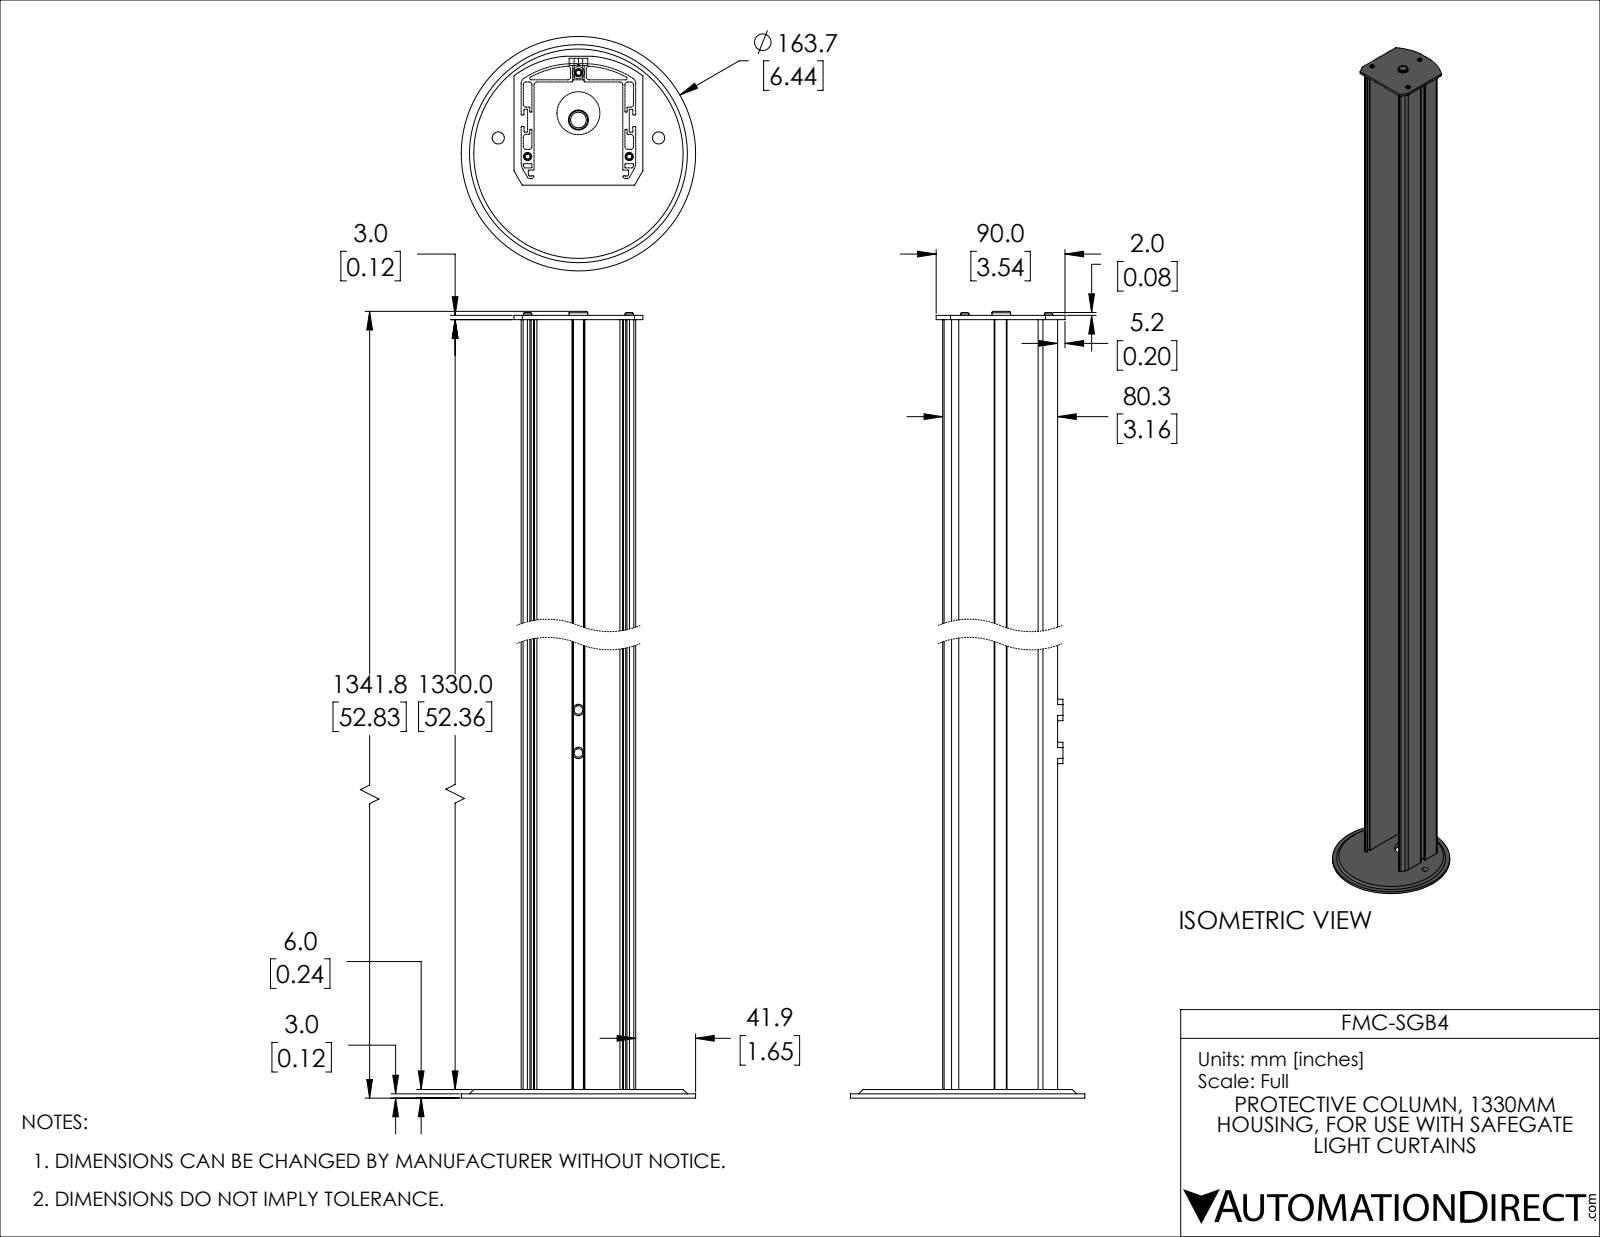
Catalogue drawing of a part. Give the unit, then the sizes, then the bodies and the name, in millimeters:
Units: millimetres
Overall size (bounding box): 1341.8 × 163.7 × 163.7
Round holes (diameter × count): ⌀6 ×4, ⌀4.5 ×3, ⌀5 ×3, ⌀8.5 ×3, ⌀14 ×1, ⌀30 ×1
Round bosses / shafts (diameter × count): ⌀8 ×4, ⌀5.8 ×3, ⌀3.5 ×3, ⌀163.7 ×1, ⌀13 ×1
Partial cylindrical surfaces — rounded edges, fillets, slot ends (radius × count): R0.5 ×59, R2 ×22, R1 ×2, R4 ×2, R10 ×2, R62.1 ×2, R63.5 ×2, R68.5 ×2
Main face-to-face distances: 1.5, 71, 7.5, 9, 3, 72.5, 4.5, 6, 63.5, 62
Hole centre spacings: 24.3, 30, 43.7, 46.6, 57.4, 58.6, 68.4, 72.2
Volume: 1 392 000 mm³ · Surface area: 1 235 000 mm²
Bodies: 11 solids, 266 faces (141 planar, 120 cylindrical, 5 other)
Part name (STEP PRODUCT): FMC-SGB4
STEP written by: SolidWorks 2019 (AUTOMOTIVE_DESIGN)
